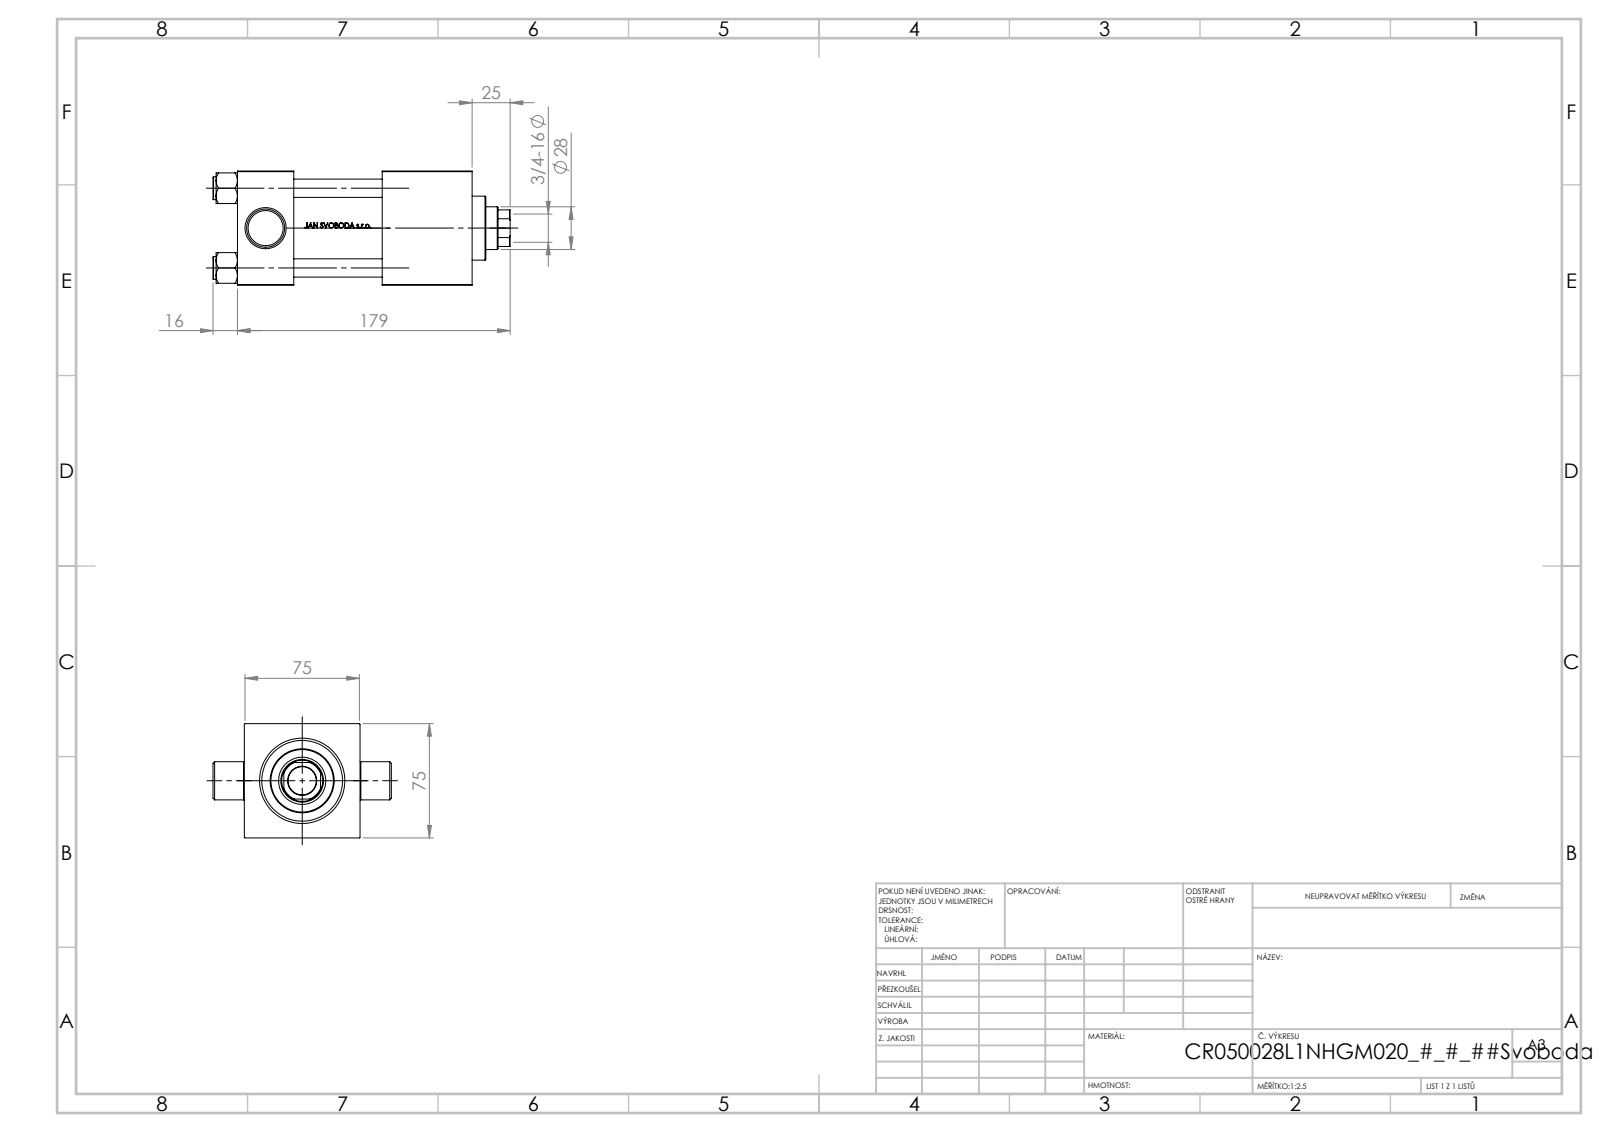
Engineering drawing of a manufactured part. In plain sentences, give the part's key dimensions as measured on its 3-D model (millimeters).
The part is named "NUT_M5_L; V215_VC_A; V215CR_VCP_L; V215CR_L_Body (+1 more)". Its 3-D file was written by "SolidWorks 2019 (CONFIG_CONTROL_DESIGN)". It is 11 solids with 1057 faces: 425 planar, 110 cylindrical and 522 other. Overall it measures 195 by 117 by 75 millimeters. Its volume is 713 380 cubic millimeters and its surface area 147 547 square millimeters. Round holes: 4 of diameter 12, 1 of diameter 7, 1 of diameter 18.5, 1 of diameter 28, 1 of diameter 31, 1 of diameter 41, 1 of diameter 50, 1 of diameter 53. Round bosses or shafts: 4 of diameter 15, 1 of diameter 56, 1 of diameter 42, 1 of diameter 25. Partial cylindrical surfaces (rounded edges, fillets, slot ends): 1 of radius 13.5. The main face-to-face distances are 75, 37, 117, 0.5, 76, 75.5, 154, 58, 59, 95. The hole center spacings are 36.98, 52.3, 73.96.
